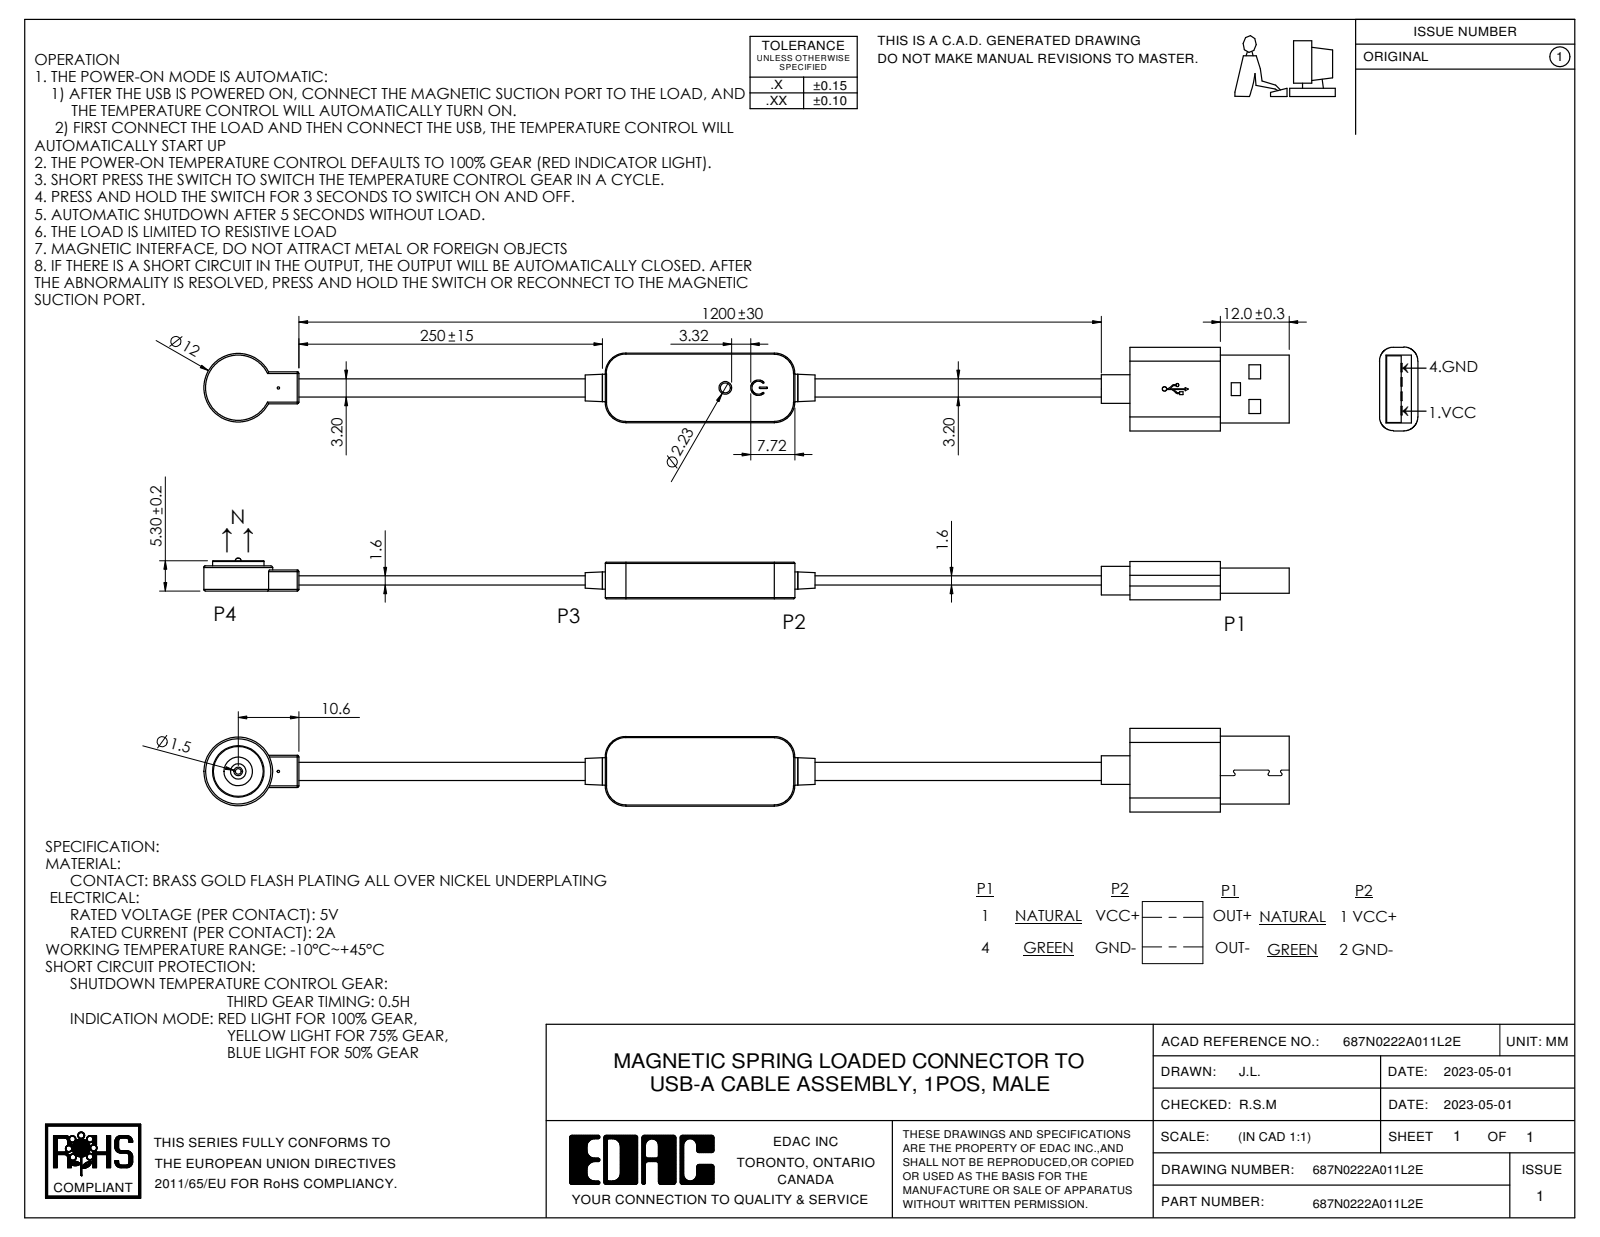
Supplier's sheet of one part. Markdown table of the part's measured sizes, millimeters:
| quantity | value |
| --- | --- |
| part name | 687N0222A011L2E |
| STEP written by | SolidWorks 2020 (AUTOMOTIVE_DESIGN) |
| units | millimeters |
| bodies | 12 solids, 214 faces (132 planar, 62 cylindrical, 20 other) |
| overall size | 189.51 × 14.6 × 7.29 |
| volume | 5 597 mm³ |
| surface area | 4 722 mm² |
| round holes (diameter × count) | 0.4 × 1, 0.57 × 1, 0.78 × 1, 1.5 × 1, 2.23 × 1, 5 × 1 |
| round bosses / shafts (diameter × count) | 12 × 1, 9 × 1, 5 × 1, 2.7 × 1, 1.75 × 1, 1 × 1 |
| partial cylindrical surfaces (radius × count) | 0.2 × 8, 0.3 × 8, 0.5 × 6, 2.44 × 4, 3.6 × 4, 0.12 × 2, 0.13 × 2, 1.12 × 1 |
| main face-to-face distances | 2.39, 3.99, 6.38, 1.6, 4.48, 7.68, 1.13, 5.57, 0.41, 2.8 |
| hole center spacings | 2.35, 7, 76.7, 78.06, 78.94, 85.06, 154.76, 157 |
